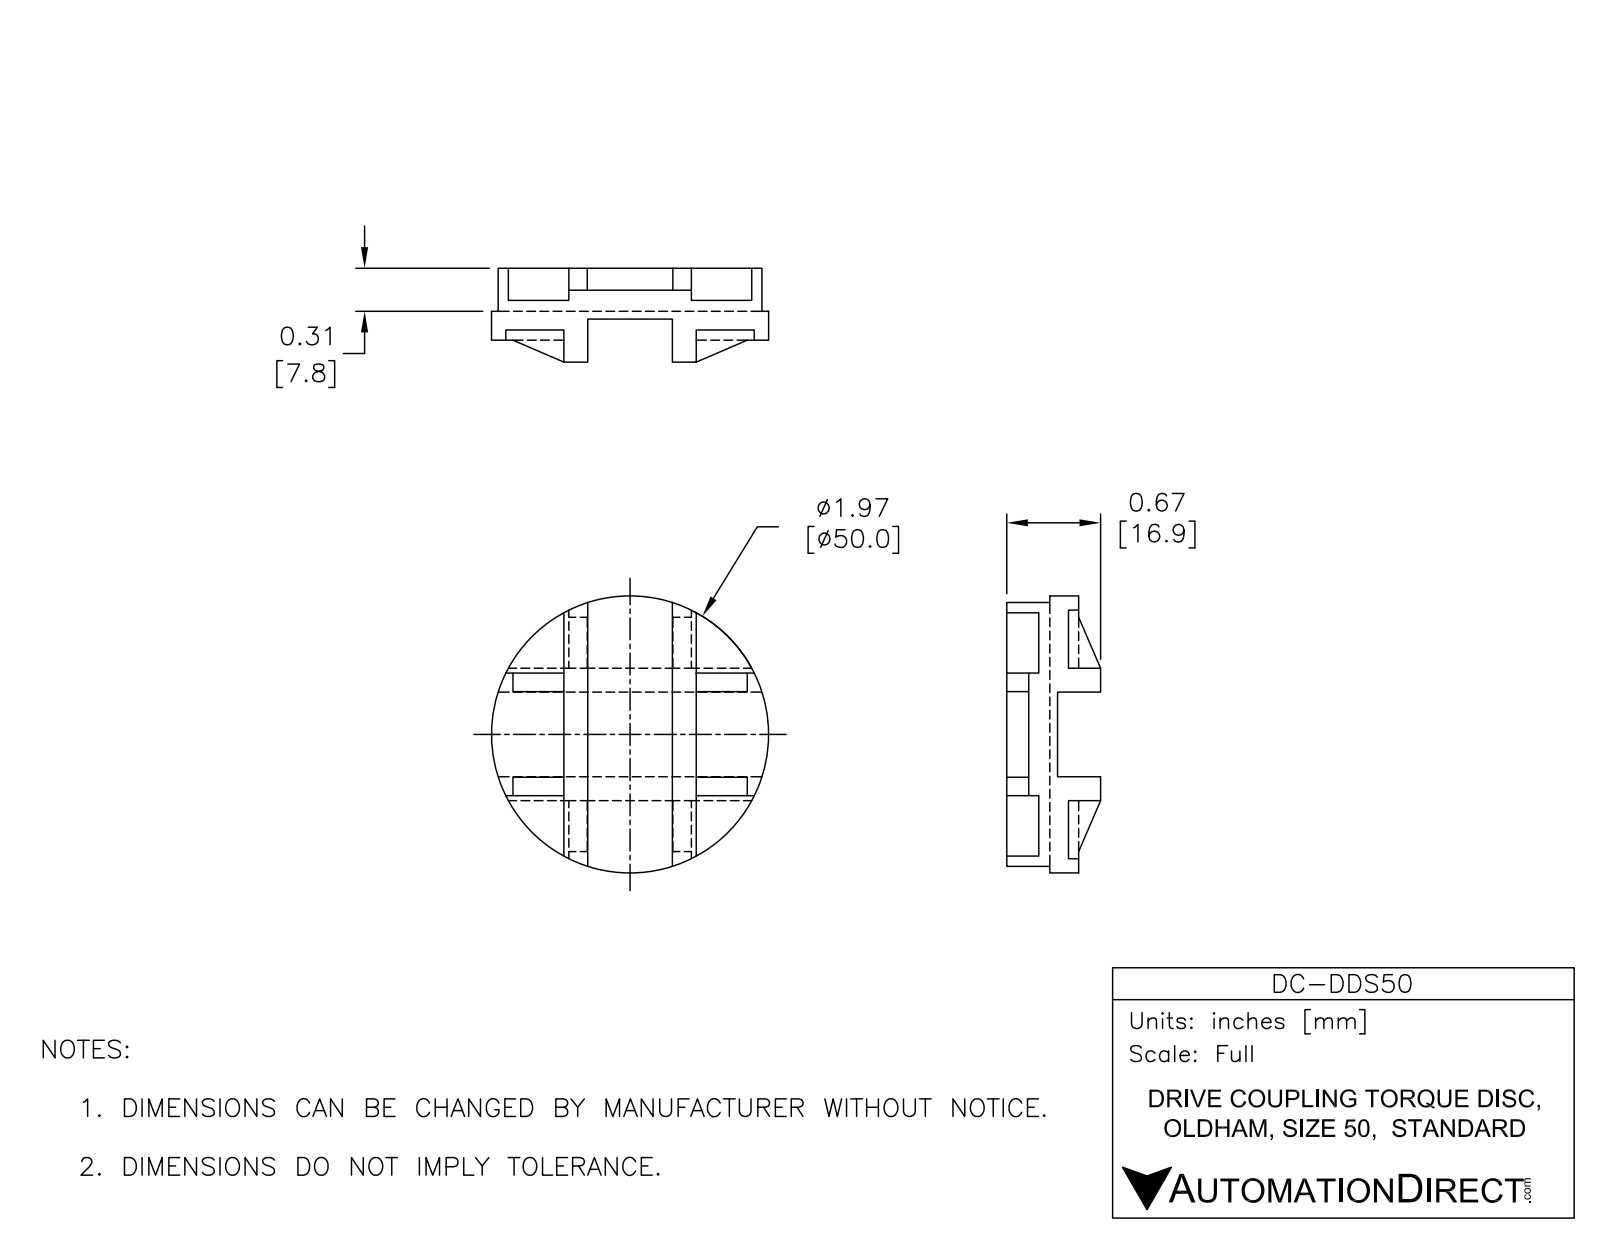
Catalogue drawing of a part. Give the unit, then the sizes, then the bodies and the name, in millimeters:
Units: millimetres
Overall size (bounding box): 50 × 50 × 16.94
Round bosses / shafts (diameter × count): ⌀50 ×1
Main face-to-face distances: 3.81, 5.21, 3.96, 7.77, 9.17, 12.98, 1.4, 15.26, 4.32, 19.58
Volume: 15 239 mm³ · Surface area: 8 138 mm²
Bodies: 1 solid, 64 faces (62 planar, 2 cylindrical, 0 other)
Part name (STEP PRODUCT): DC-DDS50
STEP written by: SolidWorks 2015 (AUTOMOTIVE_DESIGN)
